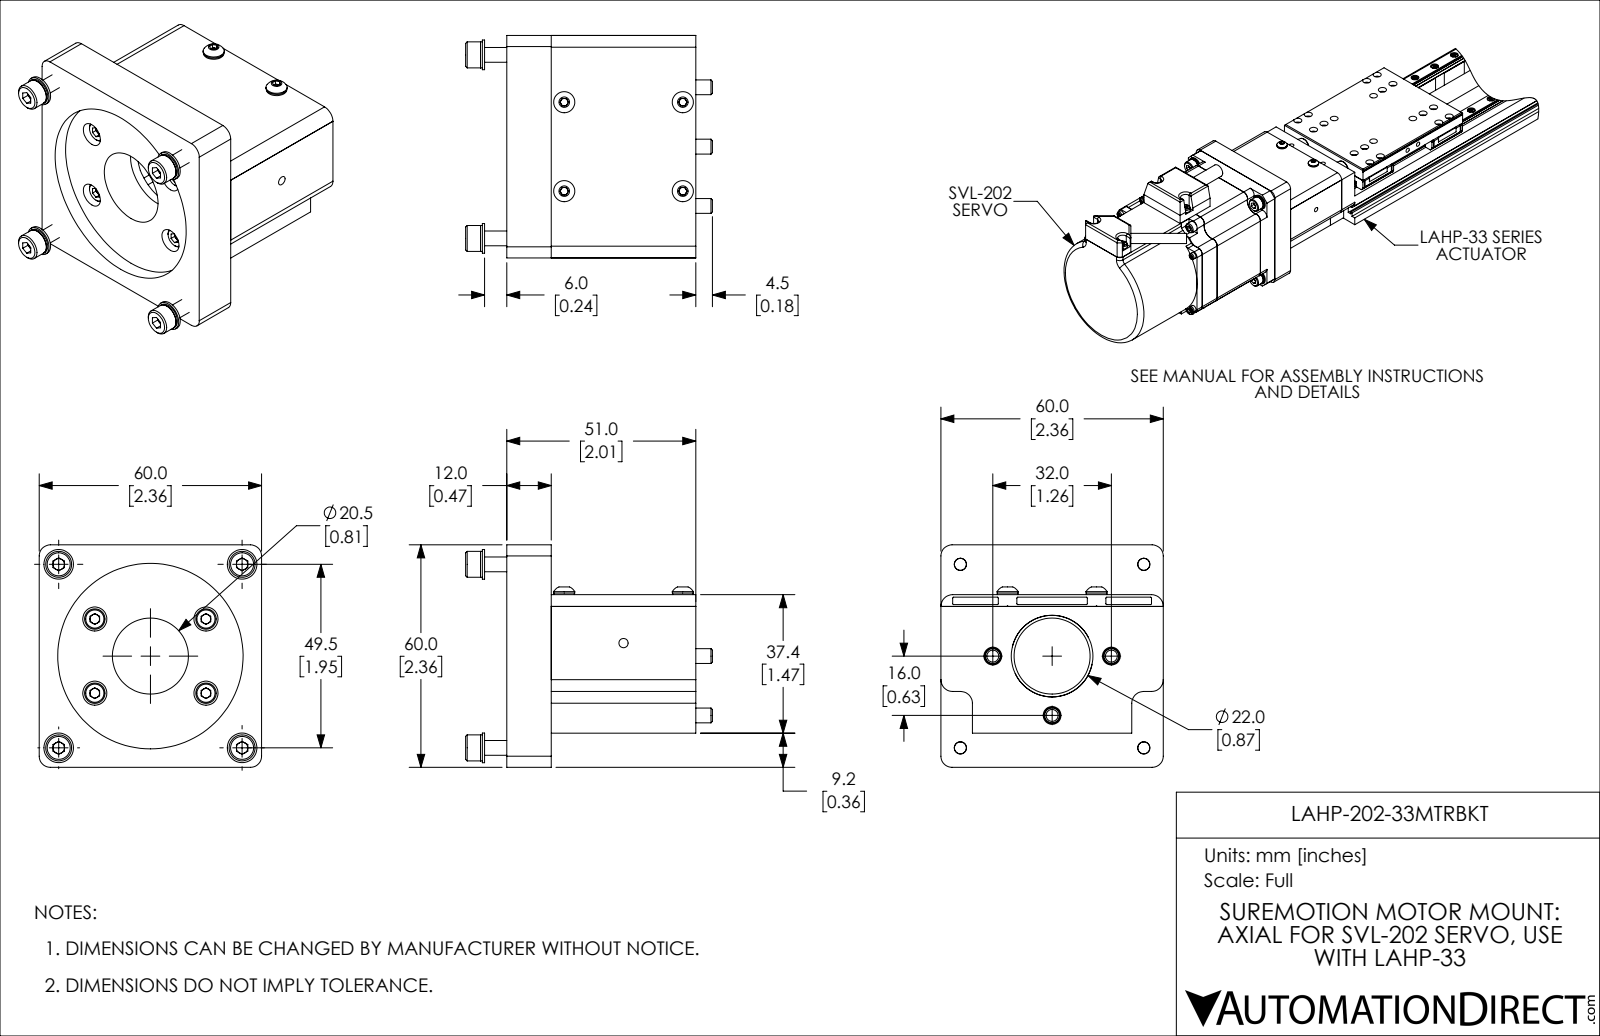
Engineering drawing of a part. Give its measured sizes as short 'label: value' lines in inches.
name: LAHP-202-33MTRBKT
written by: SolidWorks 2019 (CONFIG_CONTROL_DESIGN)
unit: in
bodies: 37 solids, 725 faces (333 planar, 256 cylindrical, 136 other)
size: 2.622 × 2.362 × 2.362
volume: 4.594 in³; area: 62.74 in²
holes: 13× ⌀0.098, 8× ⌀0.126, 8× ⌀0.142, 7× ⌀0.169, 4× ⌀0.13, 4× ⌀0.157, 4× ⌀0.256, 3× ⌀0.189, 3× ⌀0.315, 1× ⌀0.807, 1× ⌀0.867, 1× ⌀1.97
bosses: 8× ⌀0.217, 8× ⌀0.118, 7× ⌀0.276, 4× ⌀0.315, 4× ⌀0.224, 3× ⌀0.157, 1× ⌀0.866
rounds: 12× R0.01, 10× R0.125, 8× R0.118
face distances: 0.079, 0.125, 2.362, 0.02, 0.472, 0.098, 1.346, 1.471, 0.315, 0.157
hole spacings: 1.033, 1.877, 0.396, 0.406, 0.461, 0.679, 0.696, 0.71
